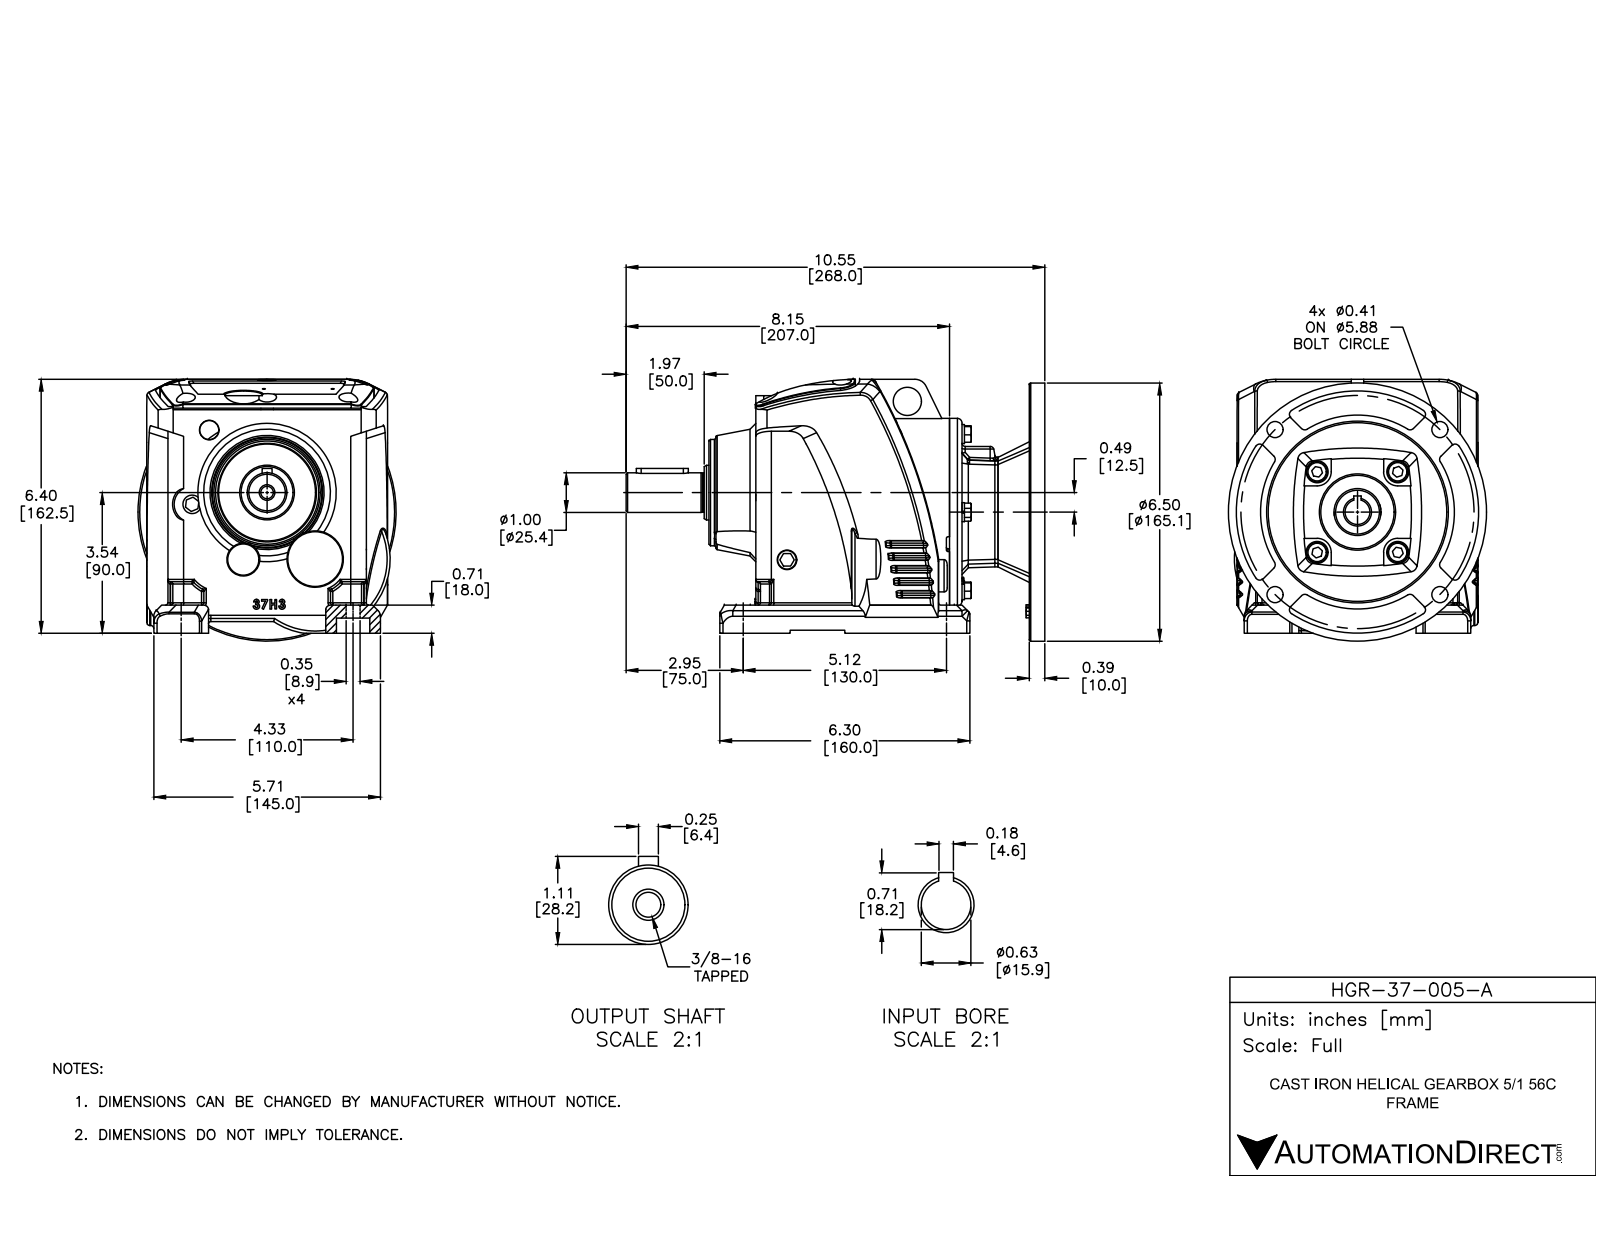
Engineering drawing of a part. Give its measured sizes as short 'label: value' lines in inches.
name: HGR-37-005-A
written by: SolidWorks 2015 (AUTOMOTIVE_DESIGN)
unit: in
bodies: 4 solids, 1036 faces (343 planar, 277 cylindrical, 416 other)
size: 10.551 × 6.596 × 6.5
volume: 169.7 in³; area: 383.8 in²
holes: 6× ⌀0.472, 4× ⌀0.406, 4× ⌀0.55, 3× ⌀0.276, 2× ⌀0.079, 2× ⌀0.354, 2× ⌀0.394, 1× ⌀0.313, 1× ⌀0.625, 1× ⌀0.709, 1× ⌀0.945, 1× ⌀1.181
bosses: 4× ⌀0.512, 4× ⌀0.48, 4× ⌀0.315, 2× ⌀1.378, 2× ⌀0.472, 1× ⌀6.5, 1× ⌀4.724, 1× ⌀2.677
rounds: 43× R0.059, 21× R0.118, 18× R0.079, 8× R0.197, 6× R0.354, 6× R0.394, 5× R0.315, 4× R0.276
face distances: 7.126, 0.236, 0.276, 0.394, 6.89, 1.102, 4.331, 0.157, 2.087, 0.079
hole spacings: 3.27, 1.437, 1.5, 2.032, 2.937, 4.154, 4.374, 1.143
